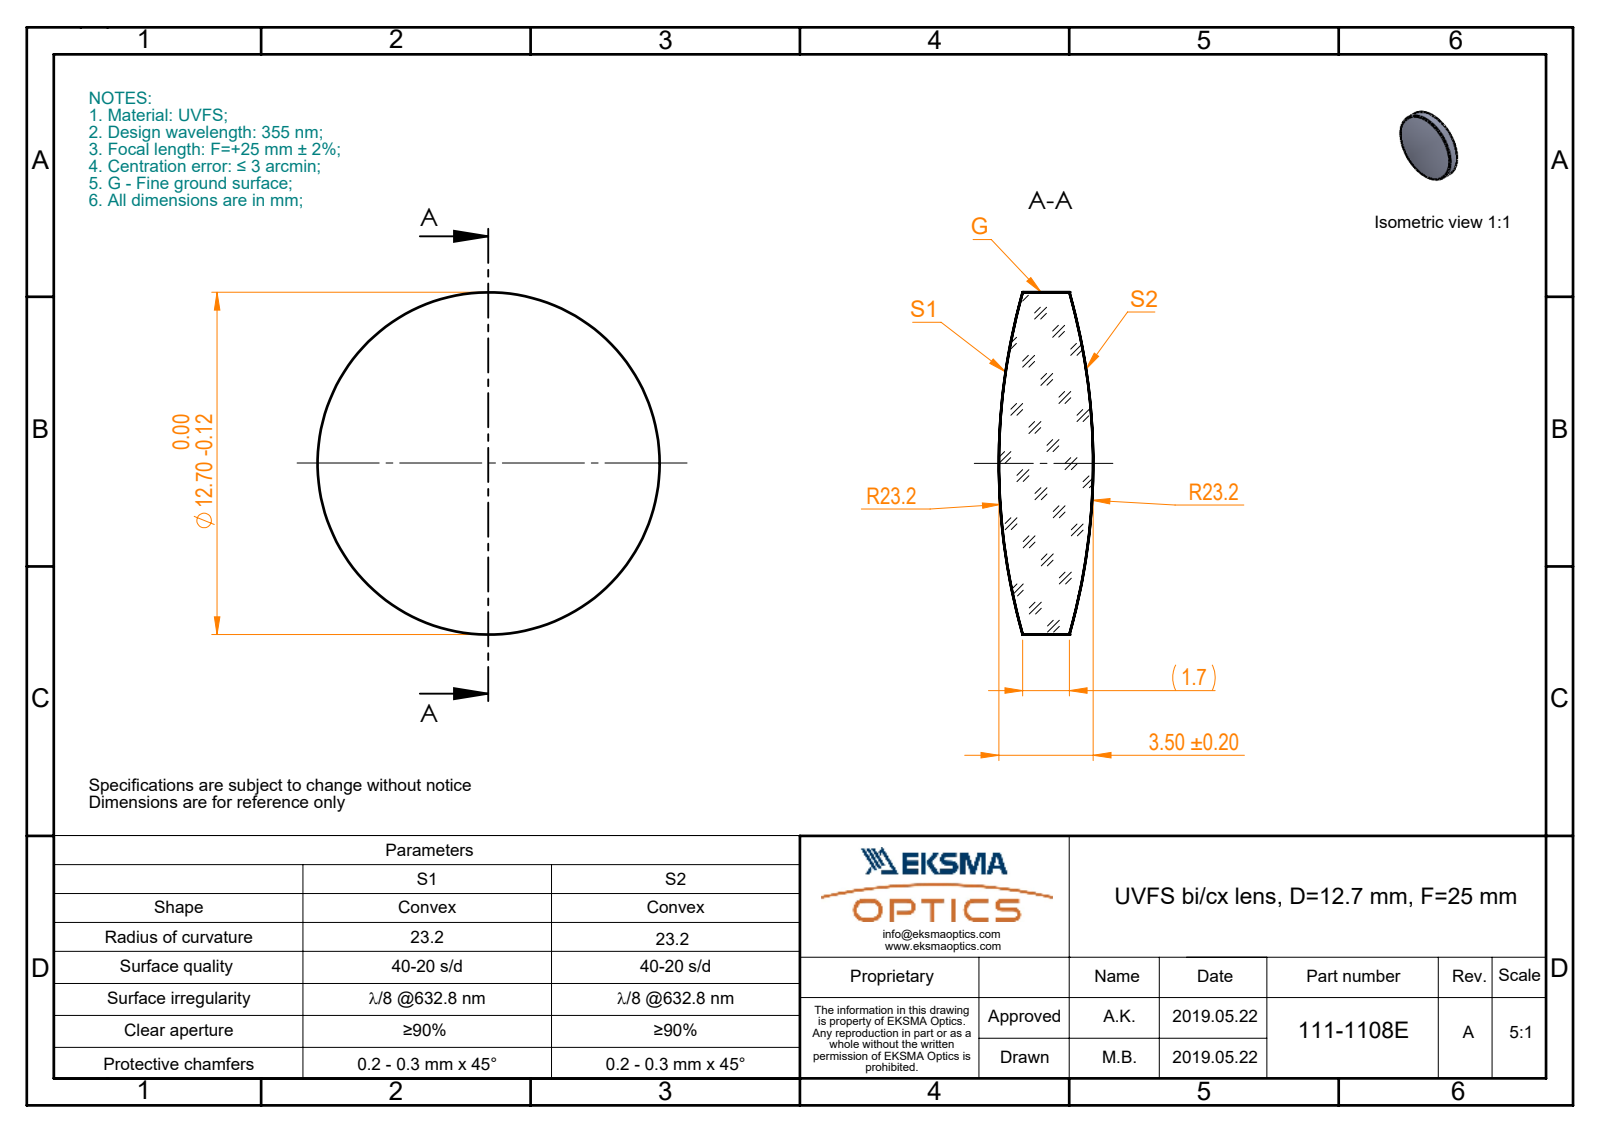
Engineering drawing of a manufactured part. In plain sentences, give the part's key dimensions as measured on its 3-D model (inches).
The part is named "111-1108E UVFS bi-cx 12.7 F25". Its 3-D file was written by "SolidWorks 2017 (CONFIG_CONTROL_DESIGN)". It is 1 solid with 6 faces: 0 planar, 2 cylindrical and 4 other. Overall it measures 0.5 by 0.5 by 0.138 inches. Its volume is 0.02 cubic inches and its surface area 0.507 square inches. Round bosses or shafts: 1 of diameter 0.5.
